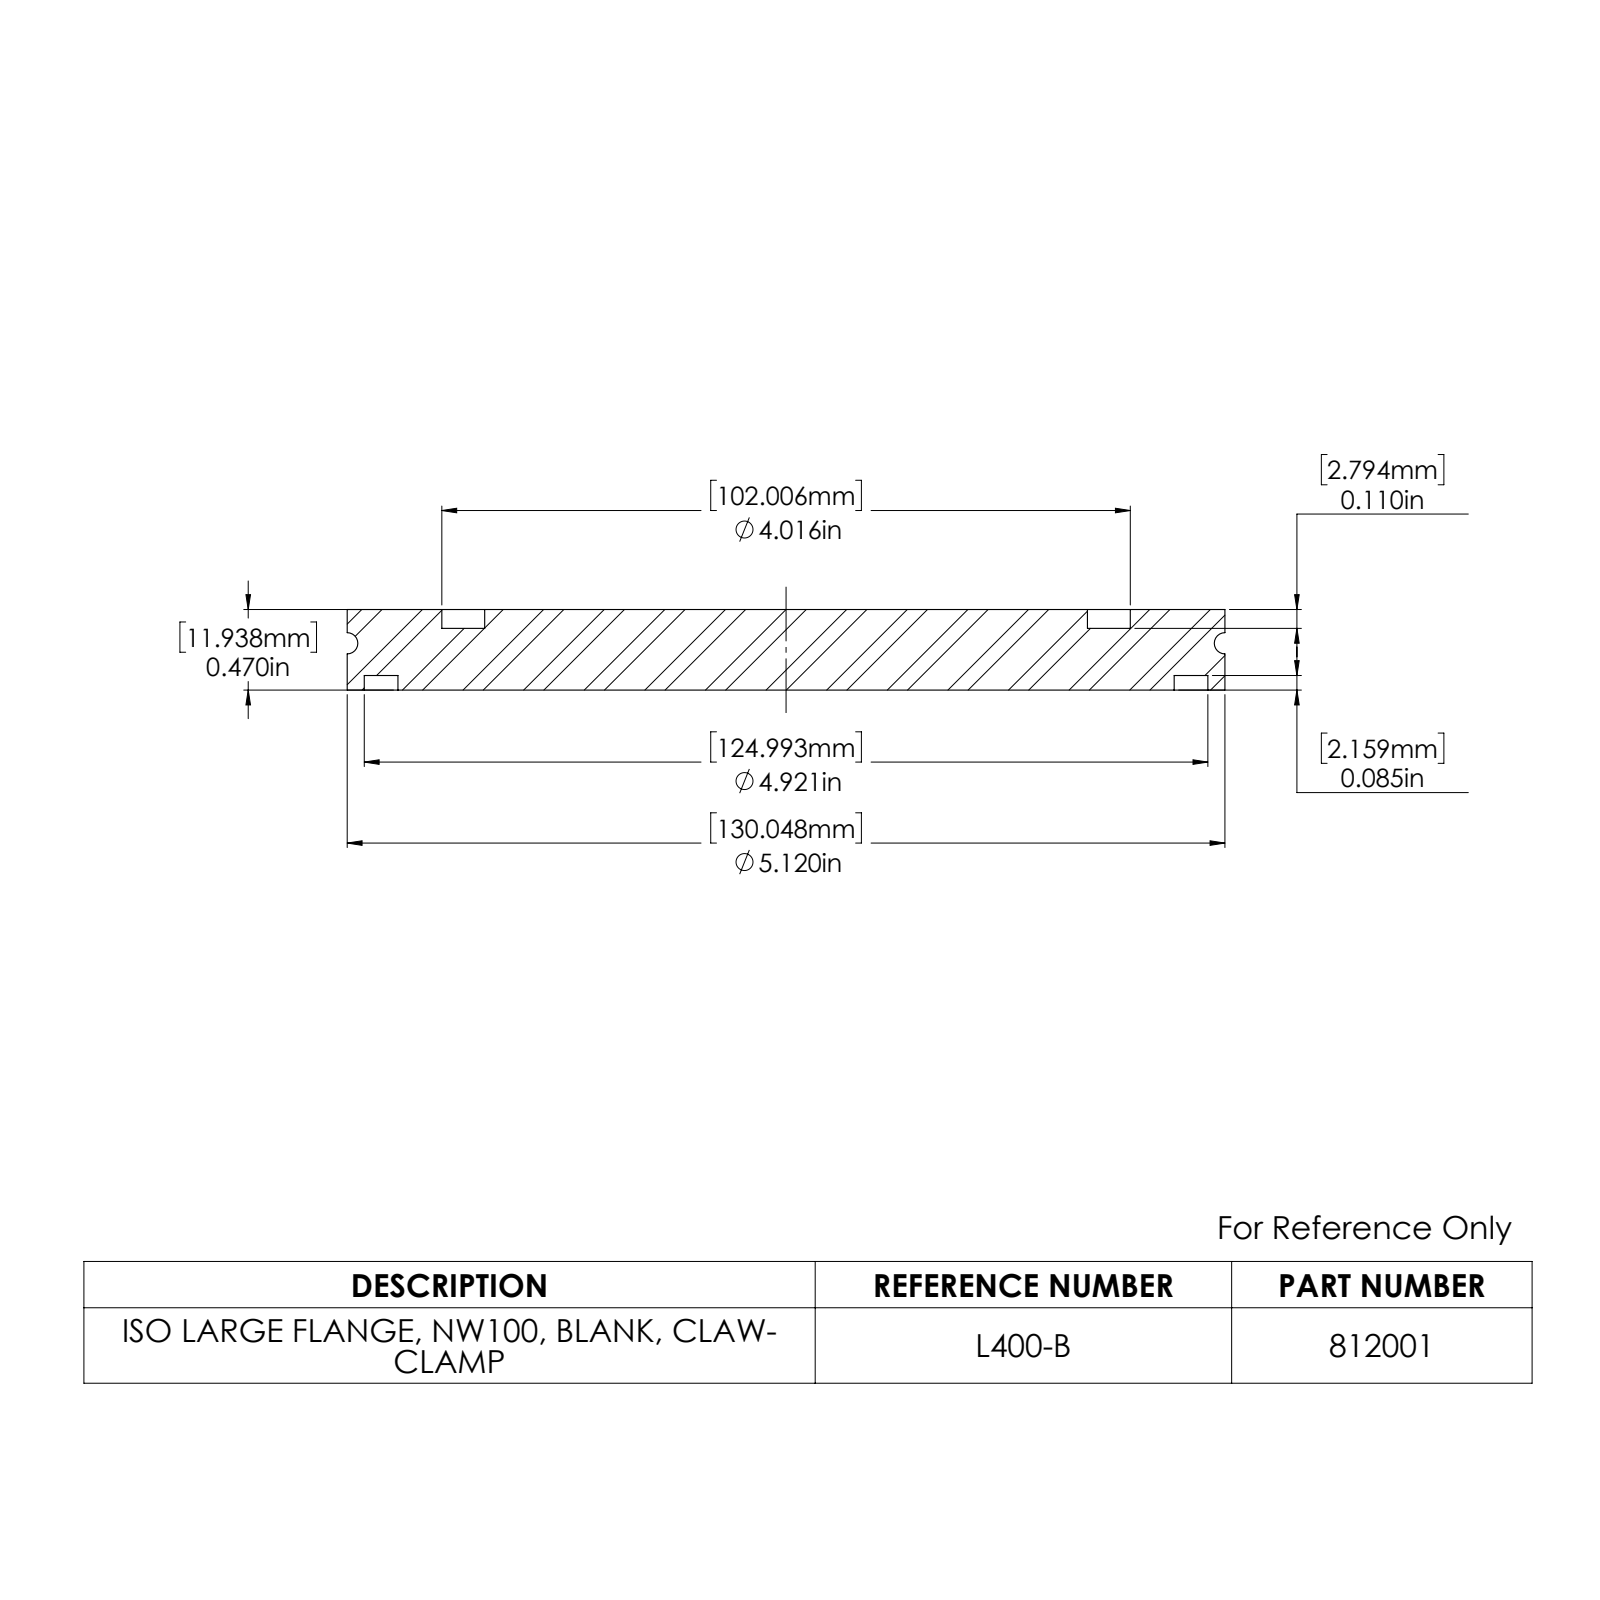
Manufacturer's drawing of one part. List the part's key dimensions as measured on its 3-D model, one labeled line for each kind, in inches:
Part name (STEP PRODUCT): 812001
STEP written by: SolidWorks 2022 (AUTOMOTIVE_DESIGN)
Units: inches
Bodies: 1 solid, 22 faces (6 planar, 12 cylindrical, 4 other)
Overall size (bounding box): 5.12 × 5.12 × 0.47
Volume: 9.007 in³ · Surface area: 54.95 in²
Round holes (diameter × count): ⌀4.016 ×1, ⌀4.921 ×1
Round bosses / shafts (diameter × count): ⌀5.12 ×1, ⌀4.528 ×1, ⌀3.516 ×1
Main face-to-face distances: 0.47, 0.36, 0.11, 0.085, 0.275, 0.385
